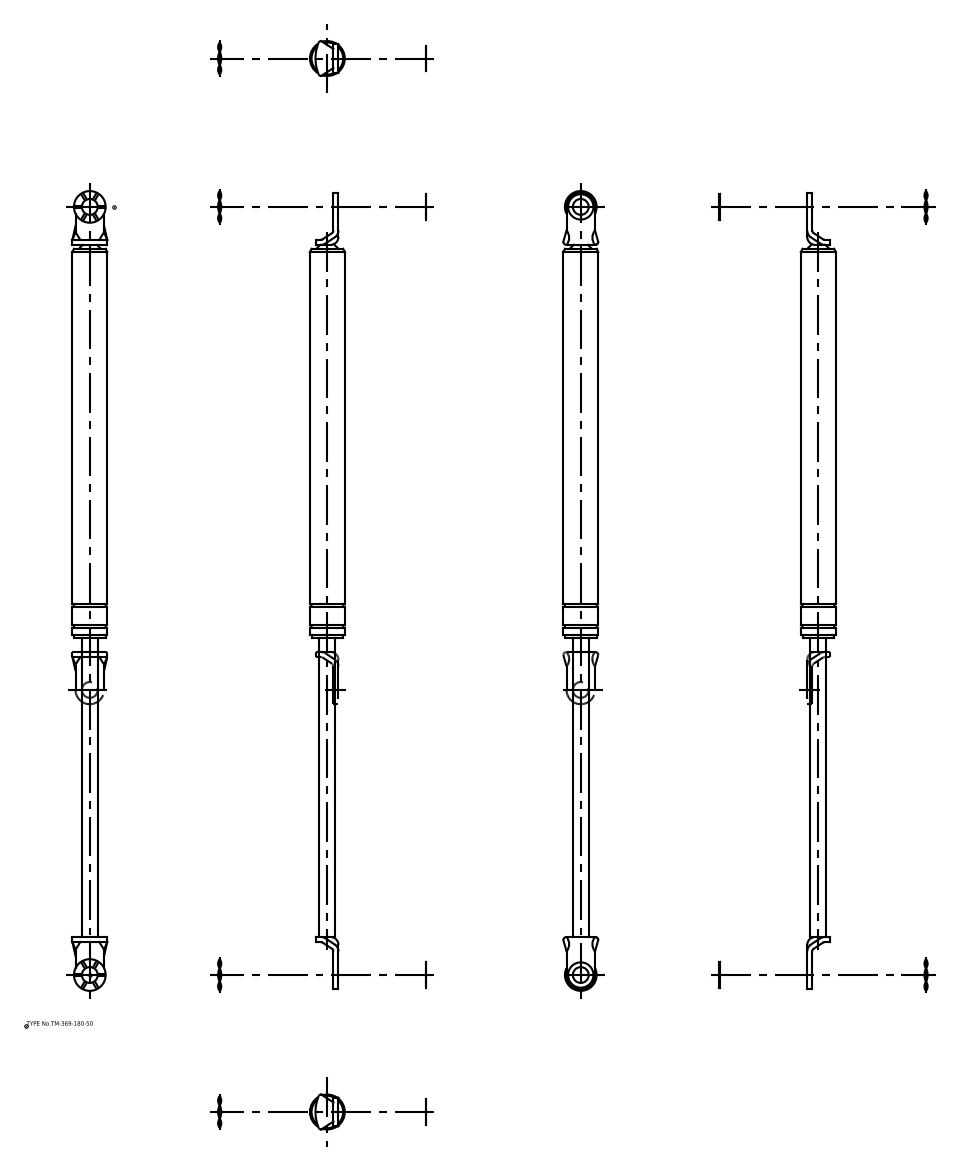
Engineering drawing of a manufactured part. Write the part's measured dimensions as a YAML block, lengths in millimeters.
part_name: "ウェーブワッシャー; ワッシャー; 本体; 本体_div"
step_written_by: "spGate 16.7.1 (AUTOMOTIVE_DESIGN)"
units: millimeters
bodies: {solids: 6, faces: 95, planar: 43, cylindrical: 44, other: 8}
overall_size: [505, 22.5, 22.5]
volume: 113862
surface_area: 29361
round_holes:
  - {diameter: 10, count: 2}
round_bosses_or_shafts:
  - {diameter: 20, count: 3}
  - {diameter: 16, count: 2}
  - {diameter: 22.5, count: 1}
  - {diameter: 22, count: 1}
  - {diameter: 10, count: 1}
partial_cylinders:
  - {radius: 4.4, count: 2}
  - {radius: 5, count: 2}
  - {radius: 9, count: 2}
  - {radius: 26.32, count: 1}
face_to_face_distances: [3.2, 2, 5.2, 5.7, 440.2, 3.7, 0.5, 251.2, 192.2, 443.4]
hole_center_spacings: [485]
